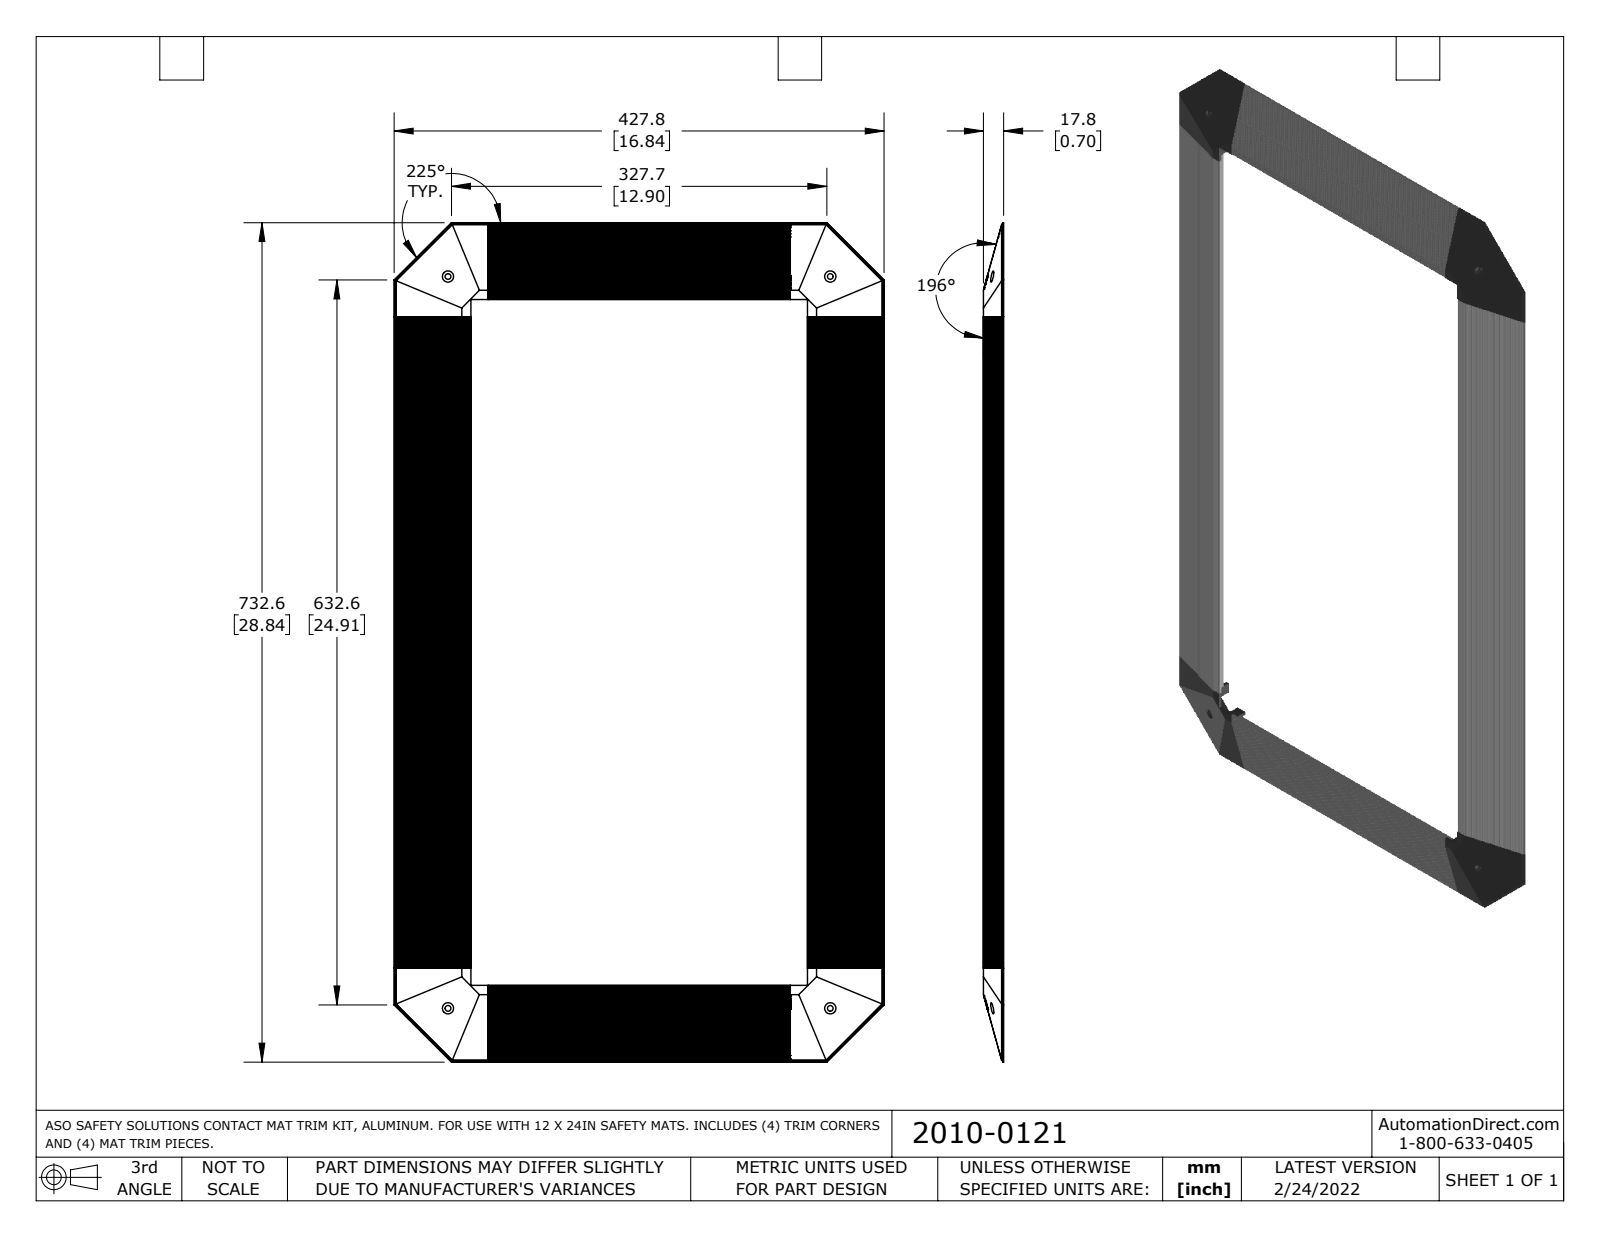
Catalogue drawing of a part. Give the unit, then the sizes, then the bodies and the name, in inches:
Units: inches
Overall size (bounding box): 28.843 × 16.843 × 0.701
Round holes (diameter × count): ⌀0.197 ×4, ⌀0.386 ×4
Round bosses / shafts (diameter × count): ⌀0.394 ×4
Partial cylindrical surfaces — rounded edges, fillets, slot ends (radius × count): R0.008 ×200, R0.039 ×112, R0.02 ×60, R0.017 ×8, R0.512 ×8, R0.291 ×4, R0.394 ×4
Main face-to-face distances: 0.076, 0.114, 0.038, 0.118, 0.19, 0.63, 0.152, 0.038, 0.079, 0.266
Hole centre spacings: 13.142, 25.142, 28.369
Volume: 34.89 in³ · Surface area: 697.8 in²
Bodies: 8 solids, 1546 faces (896 planar, 594 cylindrical, 56 other)
Part name (STEP PRODUCT): 2010-0121_Default
STEP written by: SolidWorks 2021 (CONFIG_CONTROL_DESIGN)
